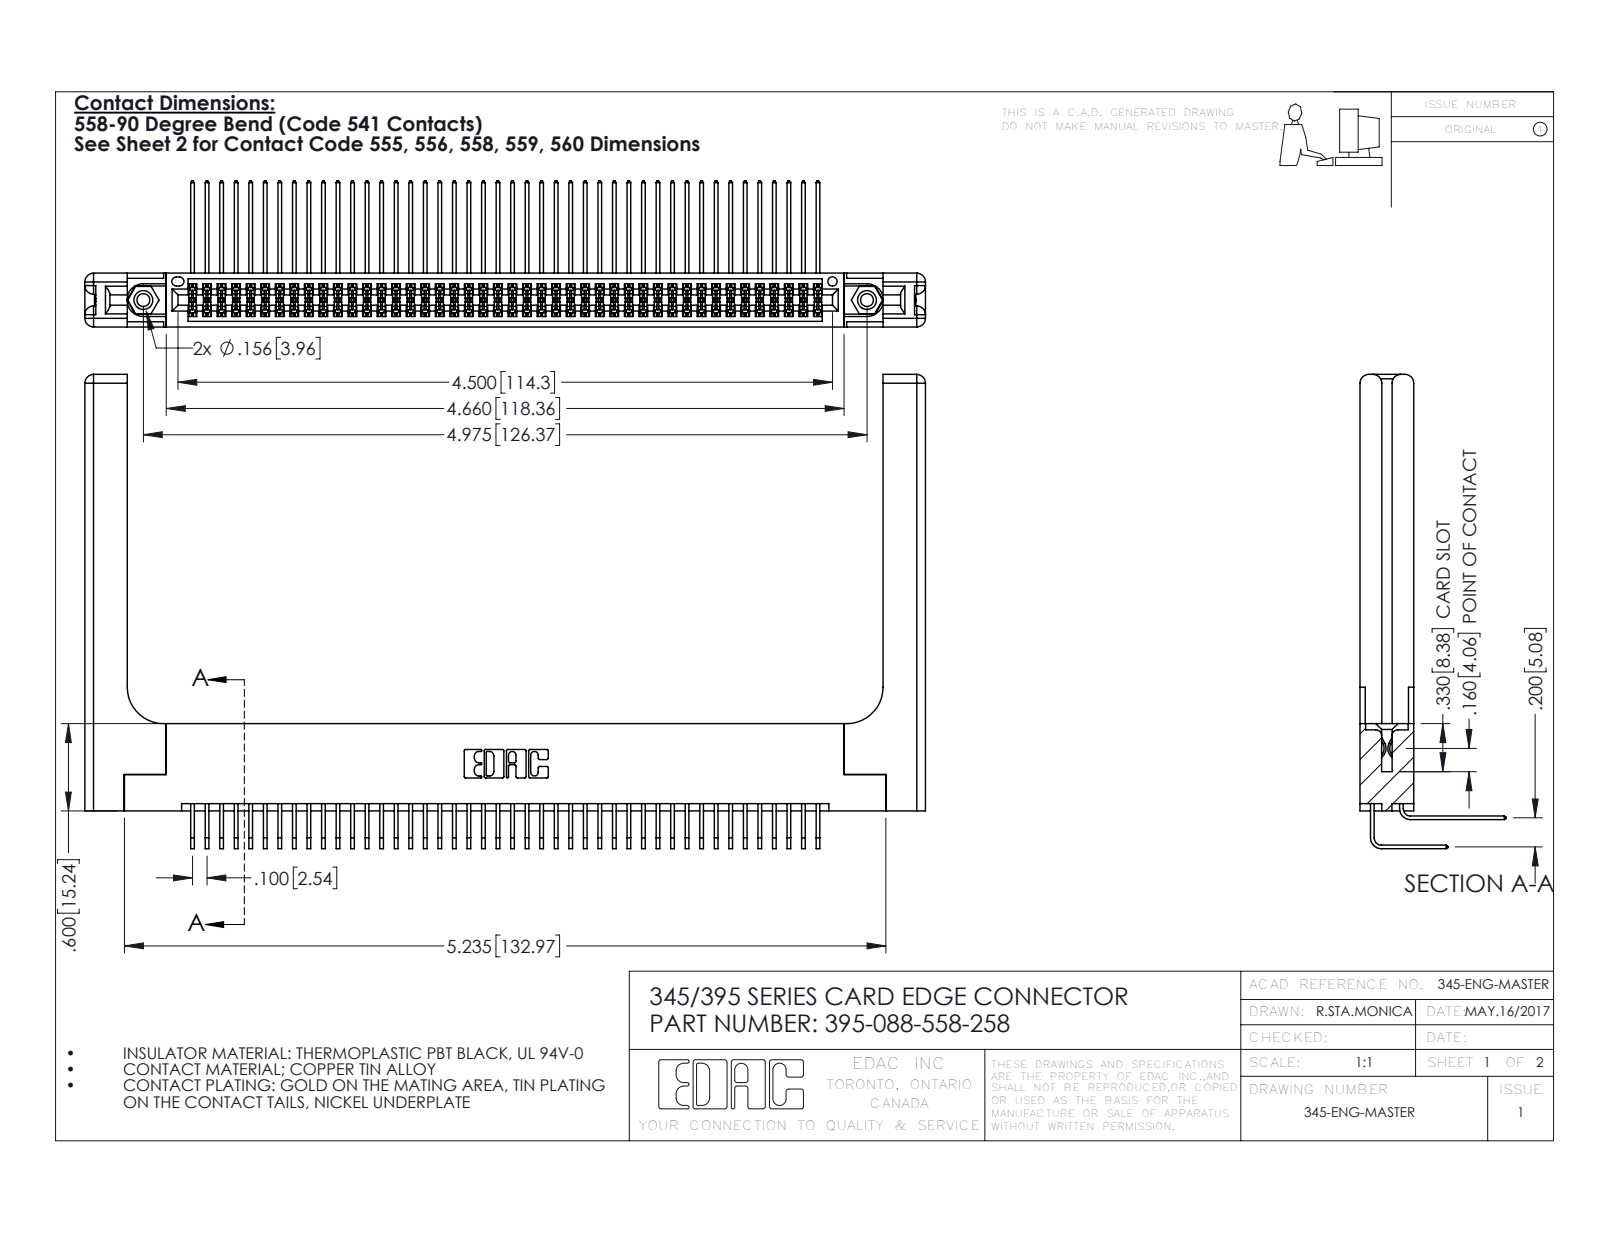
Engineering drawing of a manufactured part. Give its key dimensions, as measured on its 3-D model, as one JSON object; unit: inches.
{"part_name": "345 Part_Flush Mounting Lugs - 0.156 Dia-TH; 345-220-058_345-220-058; 345-250-001_345-250-001-102; 395-088-558-258 (+2 more)", "step_written_by": "SolidWorks 2016 (CONFIG_CONTROL_DESIGN)", "units": "inches", "bodies": {"solids": 93, "faces": 4958, "planar": 3308, "cylindrical": 1590, "other": 60}, "overall_size": [5.779, 3.259, 1.005], "volume_in3": 1.419, "surface_area_in2": 45.48, "round_holes": [[0.089, 2], [0.125, 2], [0.156, 2], [0.064, 1]], "round_bosses_or_shafts": [[0.155, 2]], "partial_cylinders_radius": [[0.006, 133], [0.01, 22], [0.06, 16], [0.007, 6], [0.031, 6], [0.026, 3], [0.014, 2], [0.019, 2]], "face_to_face_distances": [0.072, 0.298, 0.37, 0.2, 0.098, 0.272, 0.025, 0.225, 0.148, 0.15], "hole_center_spacings": [0.27, 4.739, 4.975]}
